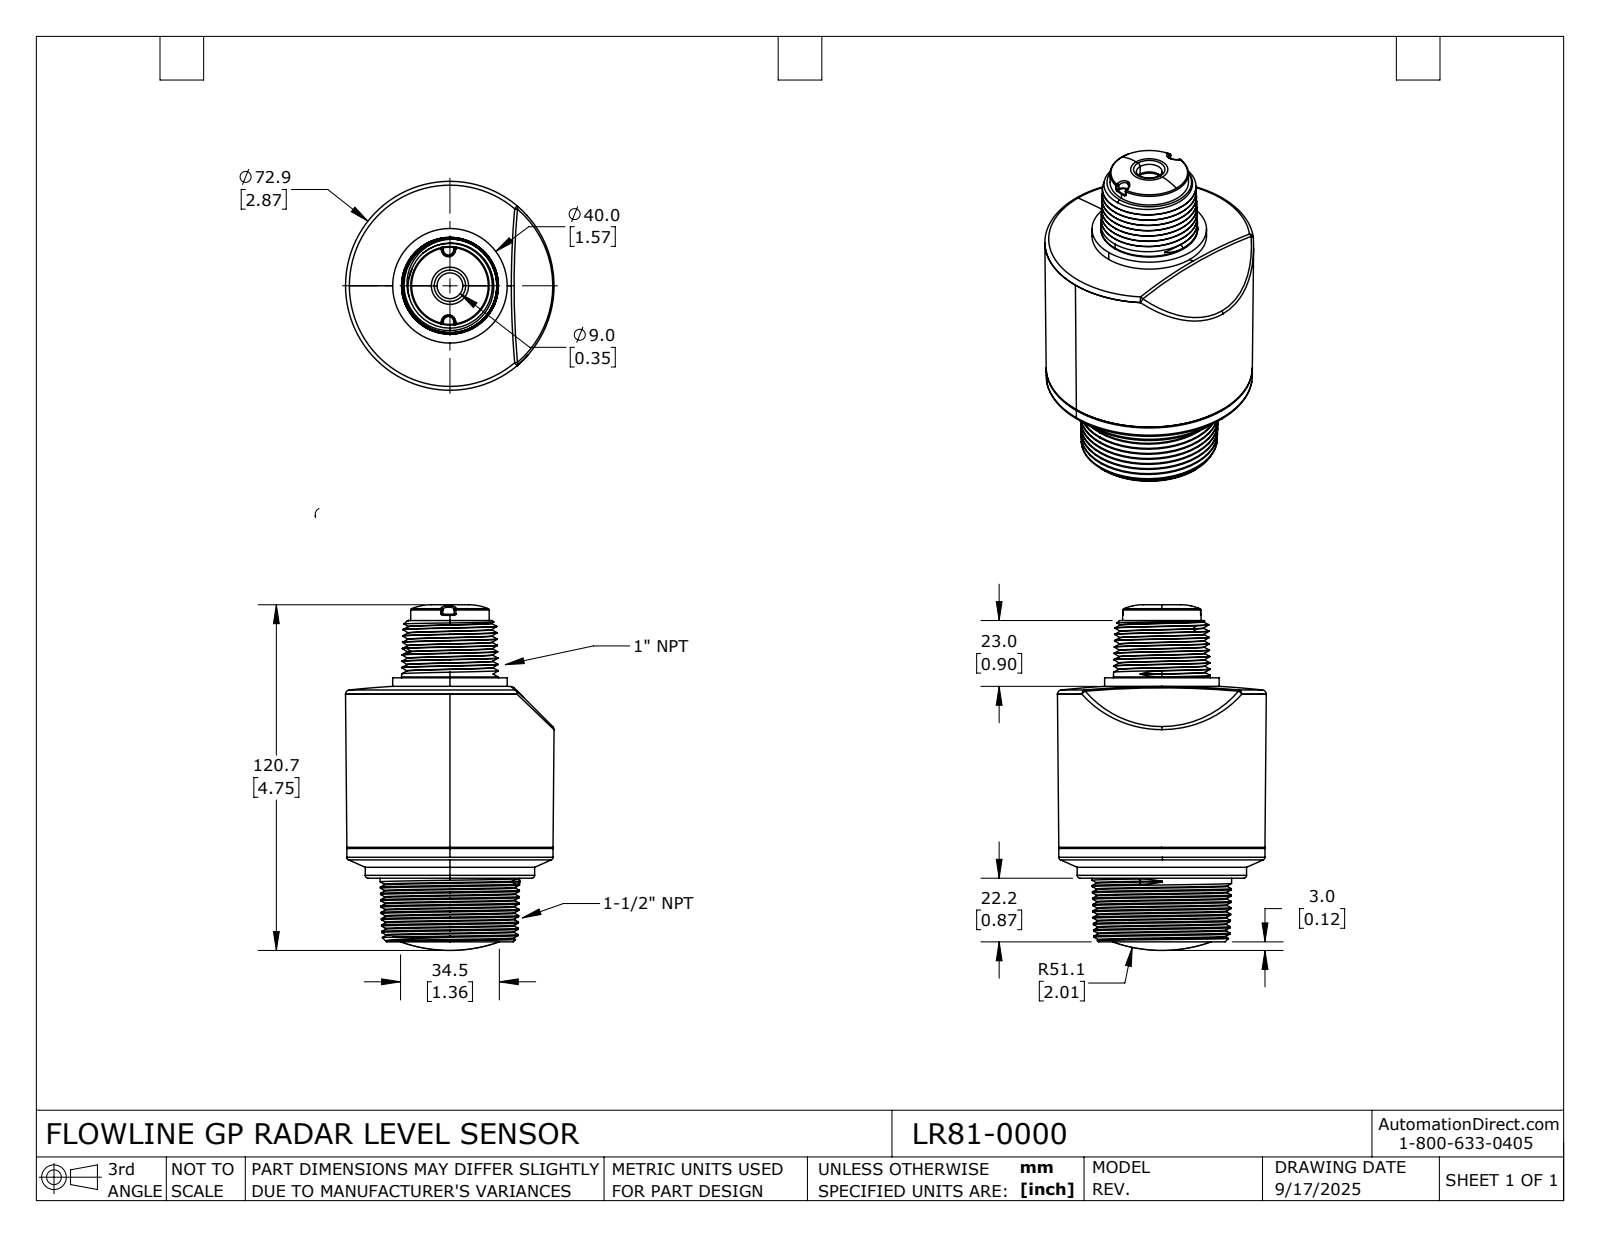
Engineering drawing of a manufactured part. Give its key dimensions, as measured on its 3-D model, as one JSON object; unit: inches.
{"part_name": "LR81-0000", "step_written_by": "SolidWorks 2024 (AUTOMOTIVE_DESIGN)", "units": "inches", "bodies": {"solids": 3, "faces": 380, "planar": 142, "cylindrical": 44, "other": 194}, "overall_size": [4.749, 2.871, 2.867], "volume_in3": 5.49, "surface_area_in2": 89.44, "round_holes": [[0.354, 1], [0.661, 1], [0.807, 1], [1.524, 1], [2.196, 1], [2.248, 1], [2.402, 1], [2.698, 1]], "round_bosses_or_shafts": [[2.835, 1], [2.329, 1], [1.575, 1], [1.331, 1], [1.079, 1], [0.866, 1], [0.795, 1]], "partial_cylinders_radius": [[0.02, 4], [0.008, 2], [0.079, 2], [0.252, 1]], "face_to_face_distances": [0.317, 0.821, 1.138, 3.219, 2.398, 2.081, 2.719, 1.898, 1.581, 0.5]}
